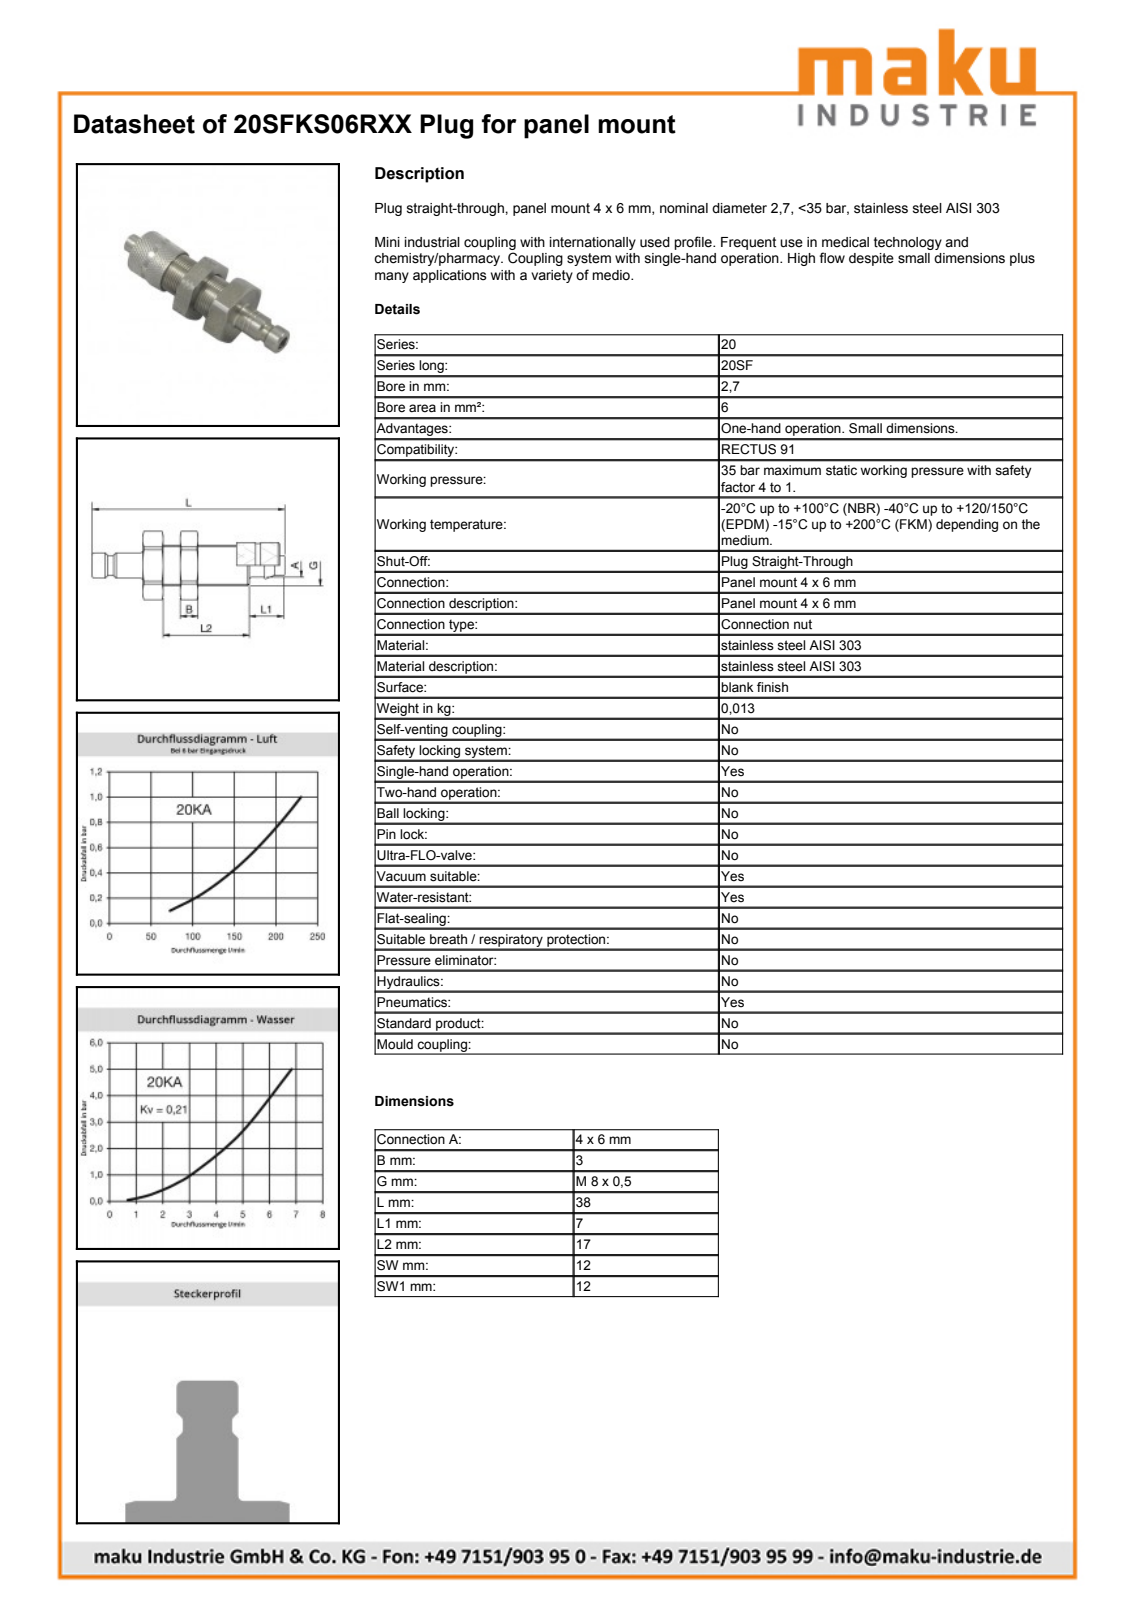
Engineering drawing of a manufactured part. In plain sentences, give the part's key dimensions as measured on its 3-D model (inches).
The part is named "D115233; D115232; D111425; D103006". Its 3-D file was written by "Autodesk Inventor 2013 (AUTOMOTIVE_DESIGN)". It is 3 solids with 126 faces: 24 planar, 37 cylindrical and 65 other. Overall it measures 1.496 by 0.531 by 0.53 inches. Its volume is 0.115 cubic inches and its surface area 3.47 square inches. Round holes: 1 of diameter 0.106, 1 of diameter 0.246, 1 of diameter 0.294, 1 of diameter 0.315. Round bosses or shafts: 1 of diameter 0.358, 1 of diameter 0.343, 1 of diameter 0.197, 1 of diameter 0.177, 1 of diameter 0.156, 1 of diameter 0.152. Partial cylindrical surfaces (rounded edges, fillets, slot ends): 1 of radius 0.266. The main face-to-face distances are 0.472, 0.157, 0.376, 0.533, 0.138, 0.238, 0.396, 0.515, 0.652, 0.891.
